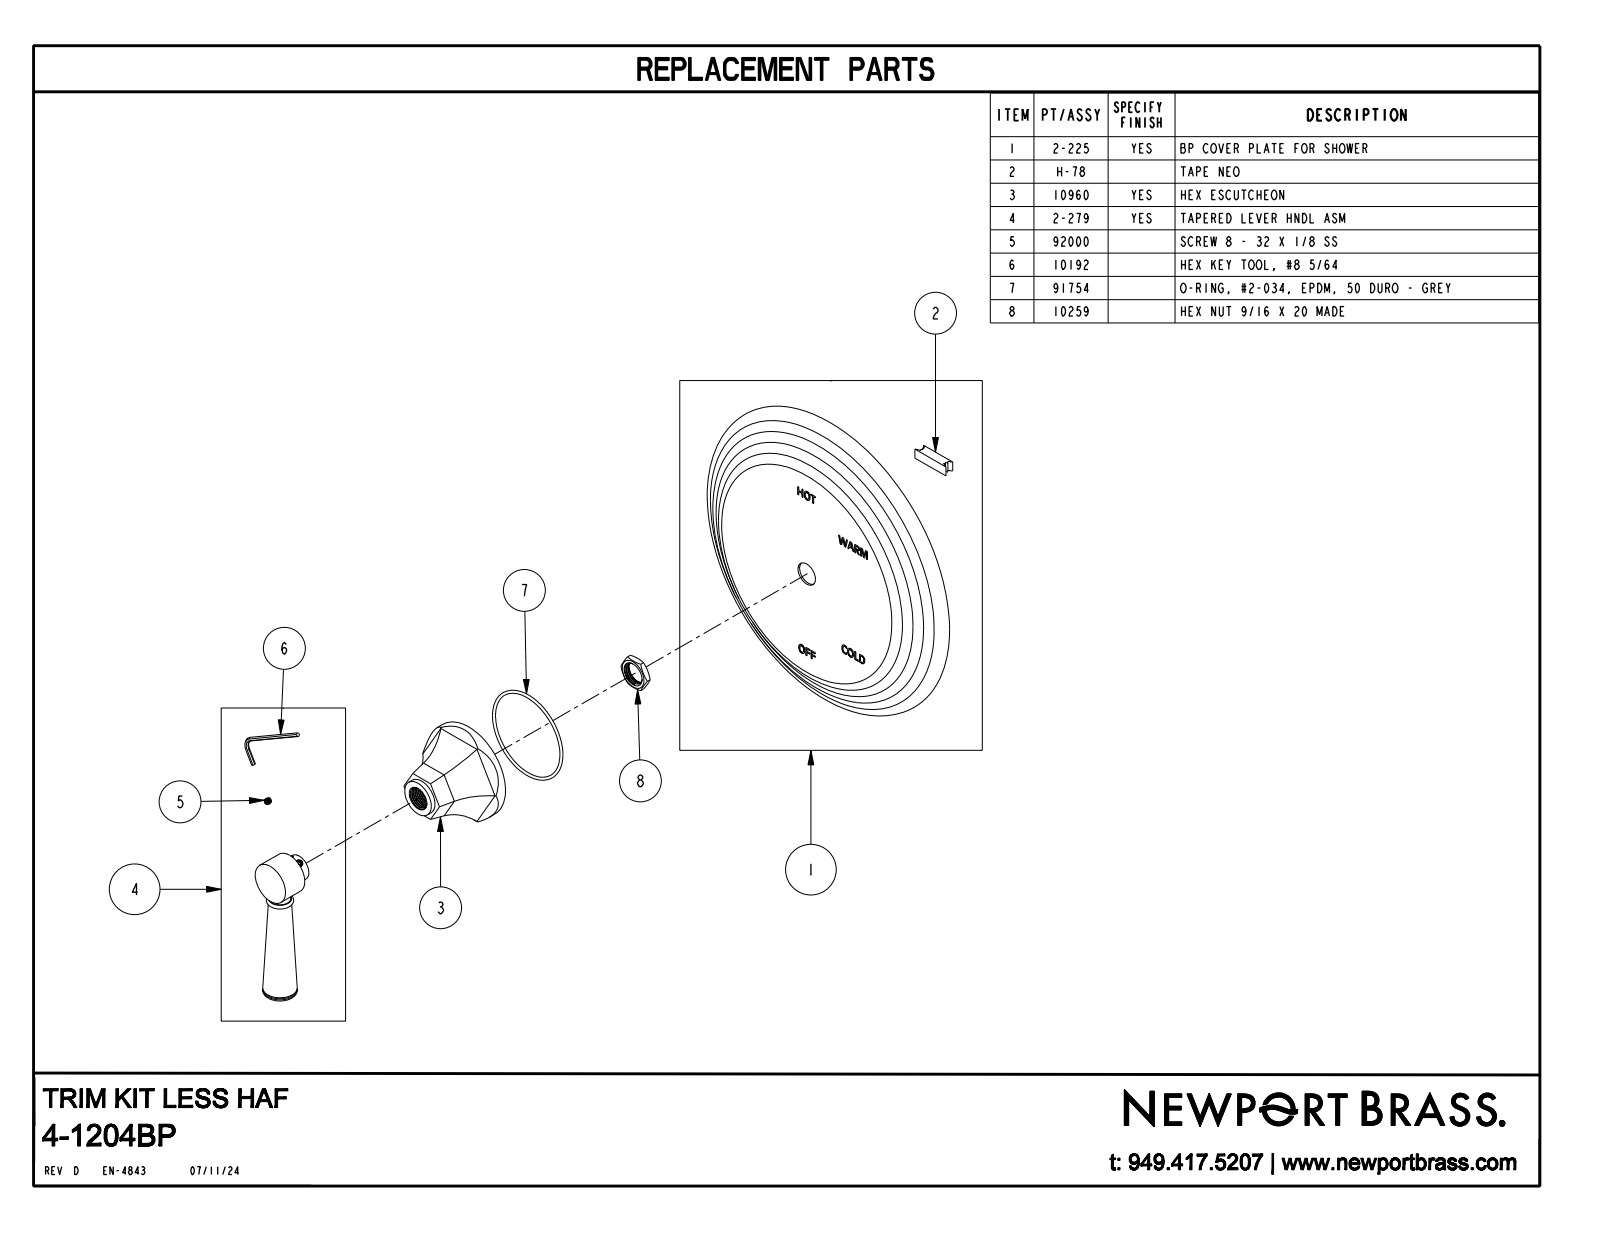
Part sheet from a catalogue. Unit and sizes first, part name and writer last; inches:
Units: inches
Overall size (bounding box): 7.75 × 7.75 × 3.436
Round holes (diameter × count): ⌀0.385 ×1
Round bosses / shafts (diameter × count): ⌀2.375 ×1, ⌀0.98 ×1, ⌀0.86 ×1, ⌀0.792 ×1, ⌀0.625 ×1, ⌀0.4 ×1, ⌀0.365 ×1
Partial cylindrical surfaces — rounded edges, fillets, slot ends (radius × count): R1.541 ×6
Main face-to-face distances: 0.754, 2.401, 1.647, 2.727, 1.973, 0.326, 2.281, 1.527, 0.12, 0.446
Volume: 32.64 in³ · Surface area: 117.6 in²
Bodies: 1 solid, 272 faces (142 planar, 22 cylindrical, 108 other)
Part name (STEP PRODUCT): 4-1204BP
STEP written by: CREO PARAMETRIC BY PTC INC, 2018400 (CONFIG_CONTROL_DESIGN)
